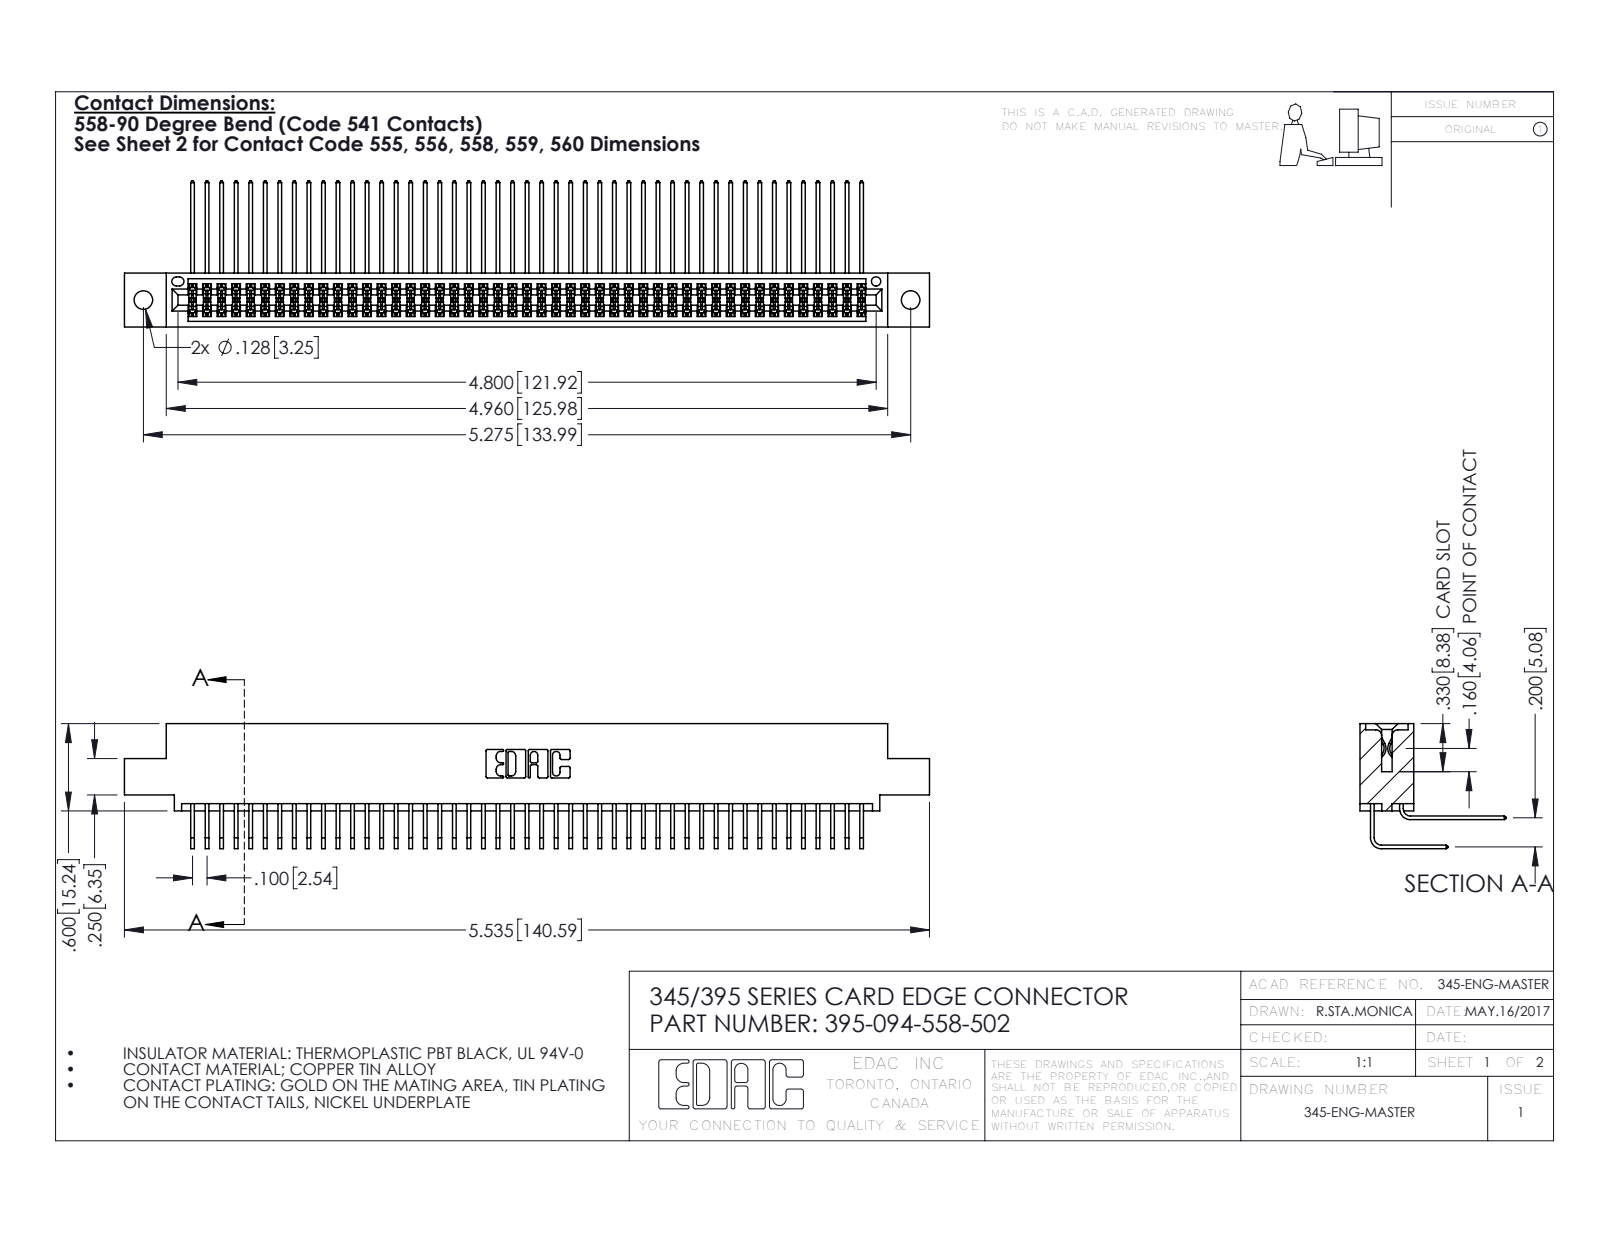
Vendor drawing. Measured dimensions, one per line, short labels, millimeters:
name: 345-292-001_558 Tail - 2; 345 Part_0.110 Offset - 0.128 Dia; 395-094-558-502; 345-292-001_558 559 Tail - 1
written by: SolidWorks 2016 (CONFIG_CONTROL_DESIGN)
unit: mm
bodies: 95 solids, 5018 faces (3374 planar, 1644 cylindrical, 0 other)
size: 140.6 × 25.5 × 21.8
volume: 14 100 mm³; area: 23 360 mm²
holes: 2× ⌀3.3, 1× ⌀1.6
rounds: 142× R0.2, 22× R0.3, 6× R0.2, 6× R0.8, 3× R0.7, 2× R0.4, 2× R0.5, 2× R0.6
face distances: 1.8, 7.6, 5.1, 9.4, 2.5, 6.9, 0.6, 5.7, 0.6, 4.4
hole spacings: 6.9, 128, 134
